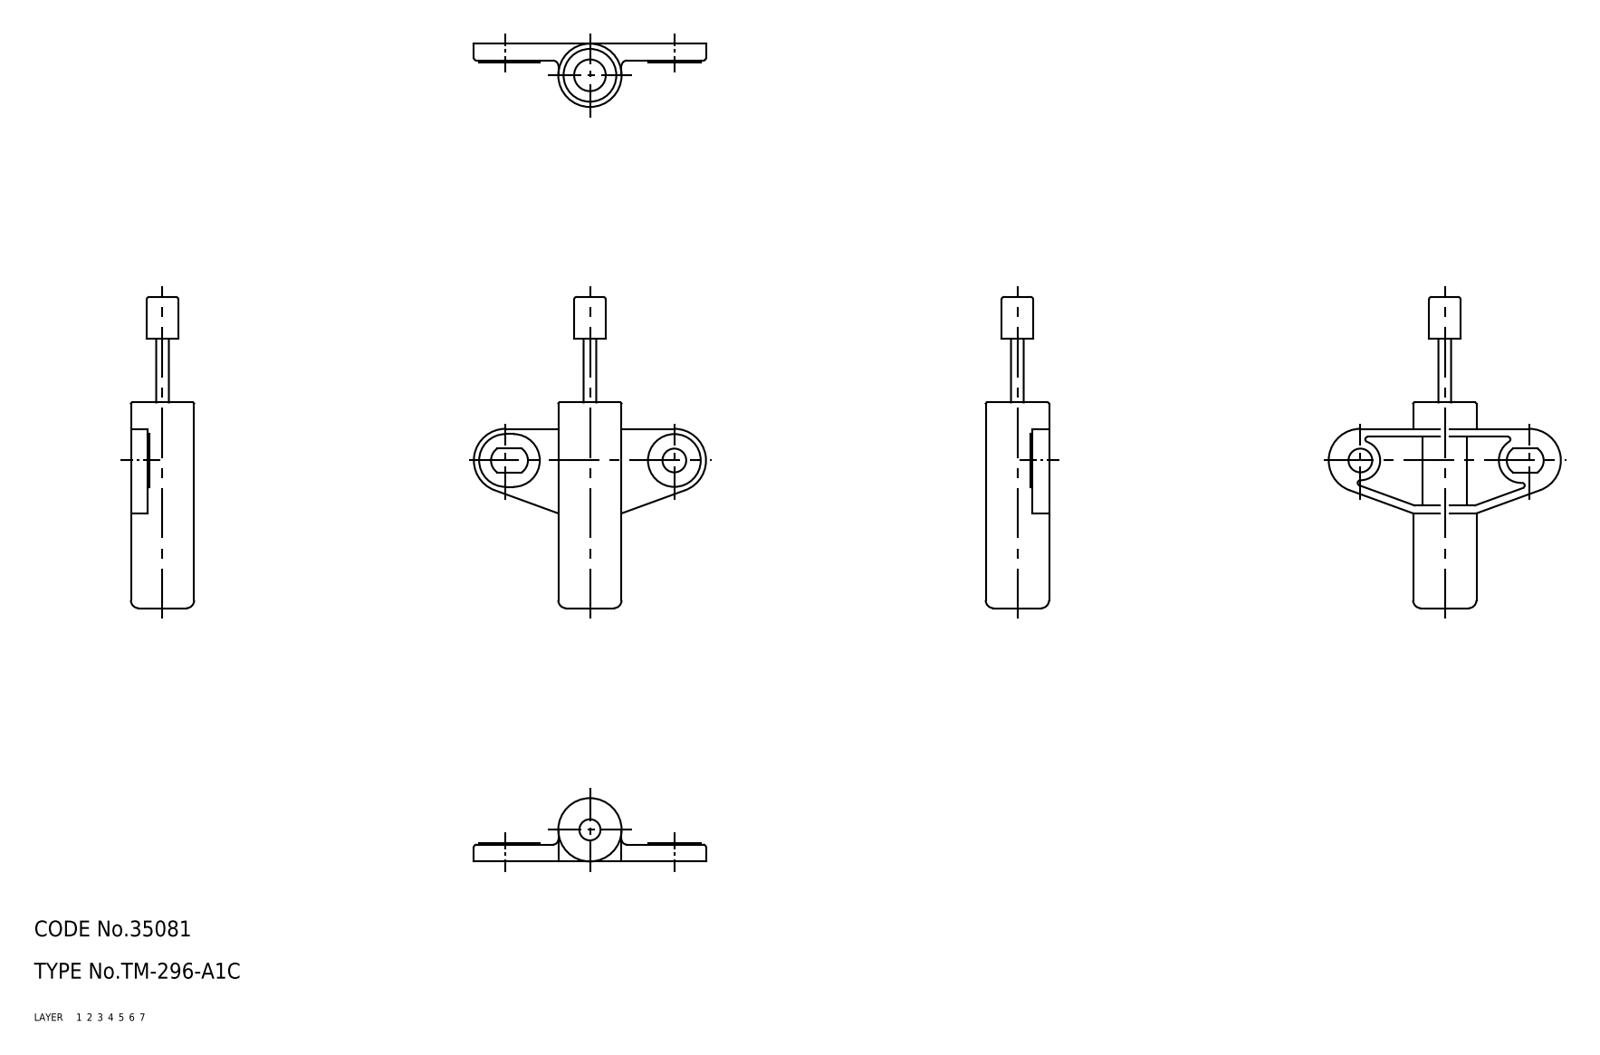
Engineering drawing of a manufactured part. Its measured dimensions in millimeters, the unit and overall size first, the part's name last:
Units: millimetres
Overall size (bounding box): 59 × 44 × 12
Volume: 5 692 mm³ · Surface area: 3 521 mm²
Bodies: 3 solids, 79 faces (0 planar, 0 cylindrical, 79 other)
Part name (STEP PRODUCT): 67113331; 67113344; 67113357
STEP written by: CADfix (AUTOMOTIVE_DESIGN)
